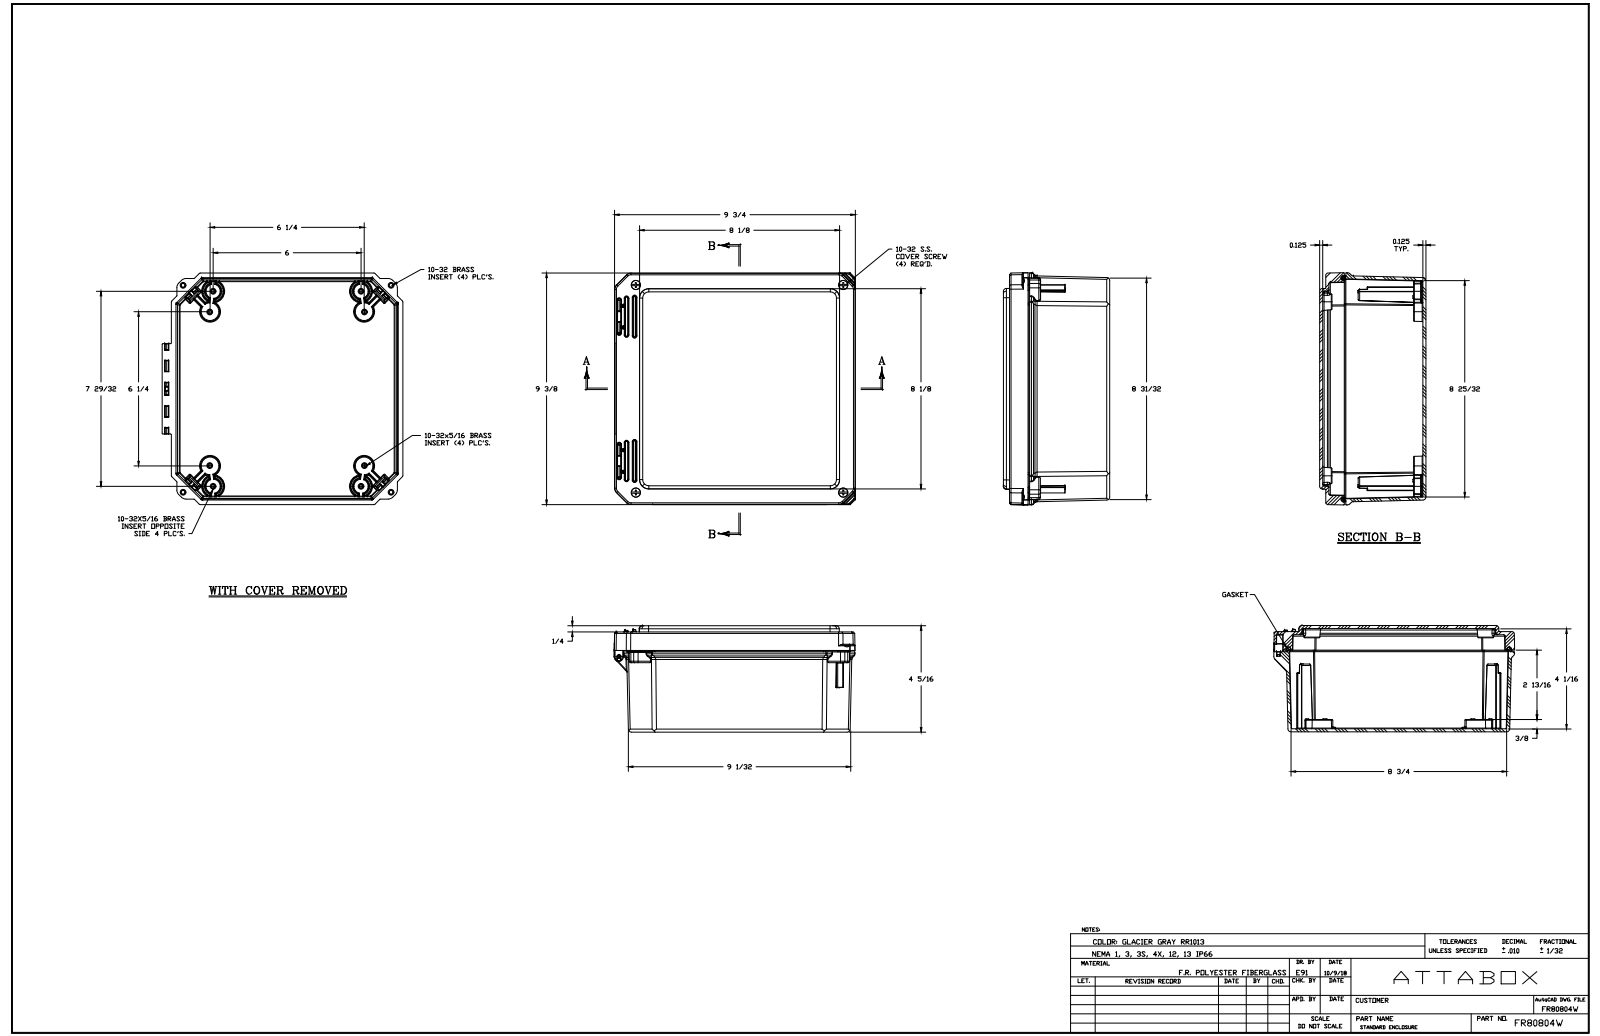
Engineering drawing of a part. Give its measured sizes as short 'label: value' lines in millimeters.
name: FR80804W
written by: SolidWorks 2018 (AUTOMOTIVE_DESIGN)
unit: mm
bodies: 27 solids, 2004 faces (669 planar, 721 cylindrical, 614 other)
size: 248.1 × 238.6 × 109.5
volume: 840 000 mm³; area: 458 300 mm²
holes: 16× ⌀4, 8× ⌀3.9, 4× ⌀6.4, 4× ⌀6.4, 2× ⌀5.6, 2× ⌀5.8, 2× ⌀8, 1× ⌀3.5
bosses: 16× ⌀6.2, 4× ⌀22.1, 4× ⌀11.4, 4× ⌀5.1, 1× ⌀11, 1× ⌀11
rounds: 109× R0.3, 80× R0.1, 65× R0.5, 42× R0.8, 24× R0.8, 24× R2.3, 24× R2.4, 22× R3.2
face distances: 3.2, 106.3, 109.5, 103.1, 3.1, 6.4, 99.9, 3.2, 9.5, 103.1
hole spacings: 169.2, 158.8, 21.3, 157, 158.8, 169.2, 179.8, 187.9
